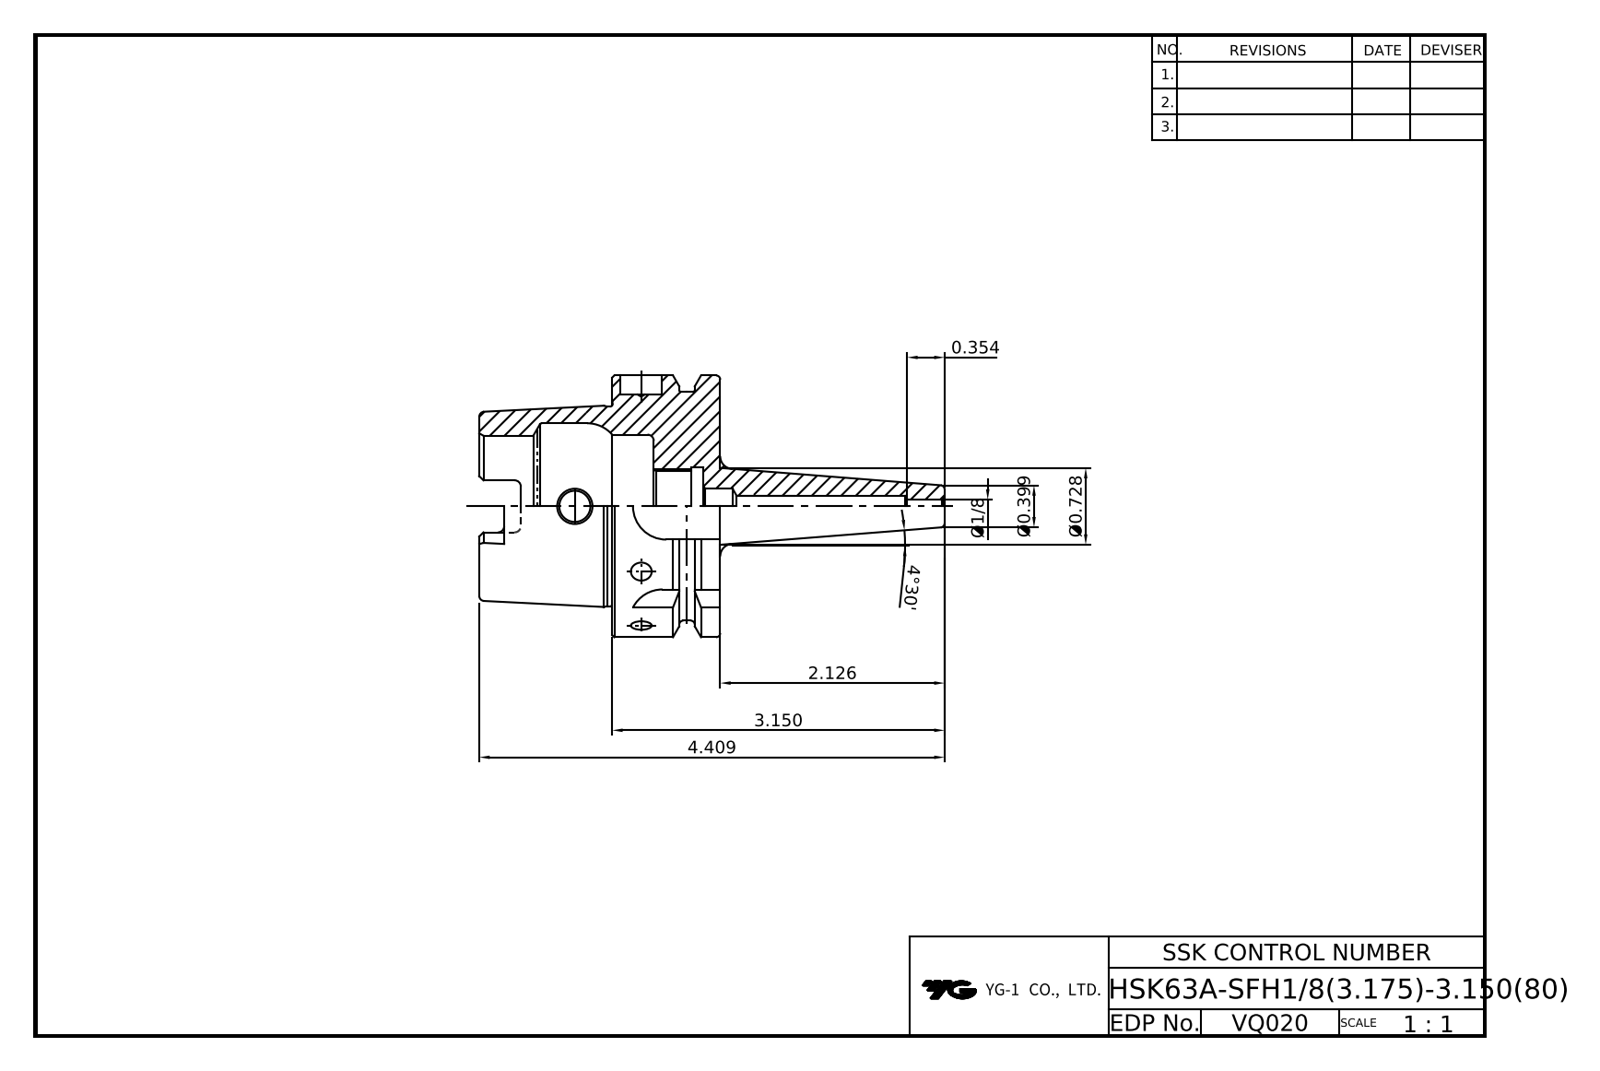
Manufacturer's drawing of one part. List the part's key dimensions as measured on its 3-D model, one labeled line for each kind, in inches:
Part name (STEP PRODUCT): LO-HSK63A-SFH3.175-80
STEP written by: Autodesk Inventor 2022 (AUTOMOTIVE_DESIGN)
Units: inches
Bodies: 1 solid, 113 faces (40 planar, 32 cylindrical, 41 other)
Overall size (bounding box): 4.409 × 2.48 × 2.48
Volume: 5.452 in³ · Surface area: 39.29 in²
Round holes (diameter × count): ⌀0.125 ×1, ⌀0.197 ×1, ⌀0.295 ×1, ⌀0.331 ×1, ⌀0.394 ×1, ⌀0.666 ×1, ⌀0.748 ×1, ⌀1.339 ×1, ⌀1.575 ×1
Round bosses / shafts (diameter × count): ⌀2.48 ×1, ⌀2.165 ×1, ⌀1.891 ×1
Partial cylindrical surfaces — rounded edges, fillets, slot ends (radius × count): R0.059 ×6, R0.113 ×4, R0.315 ×4
Main face-to-face distances: 1.024, 0.394, 0.63, 1.26, 2.283, 1.654, 2.087, 0.866, 0.157, 2.126
